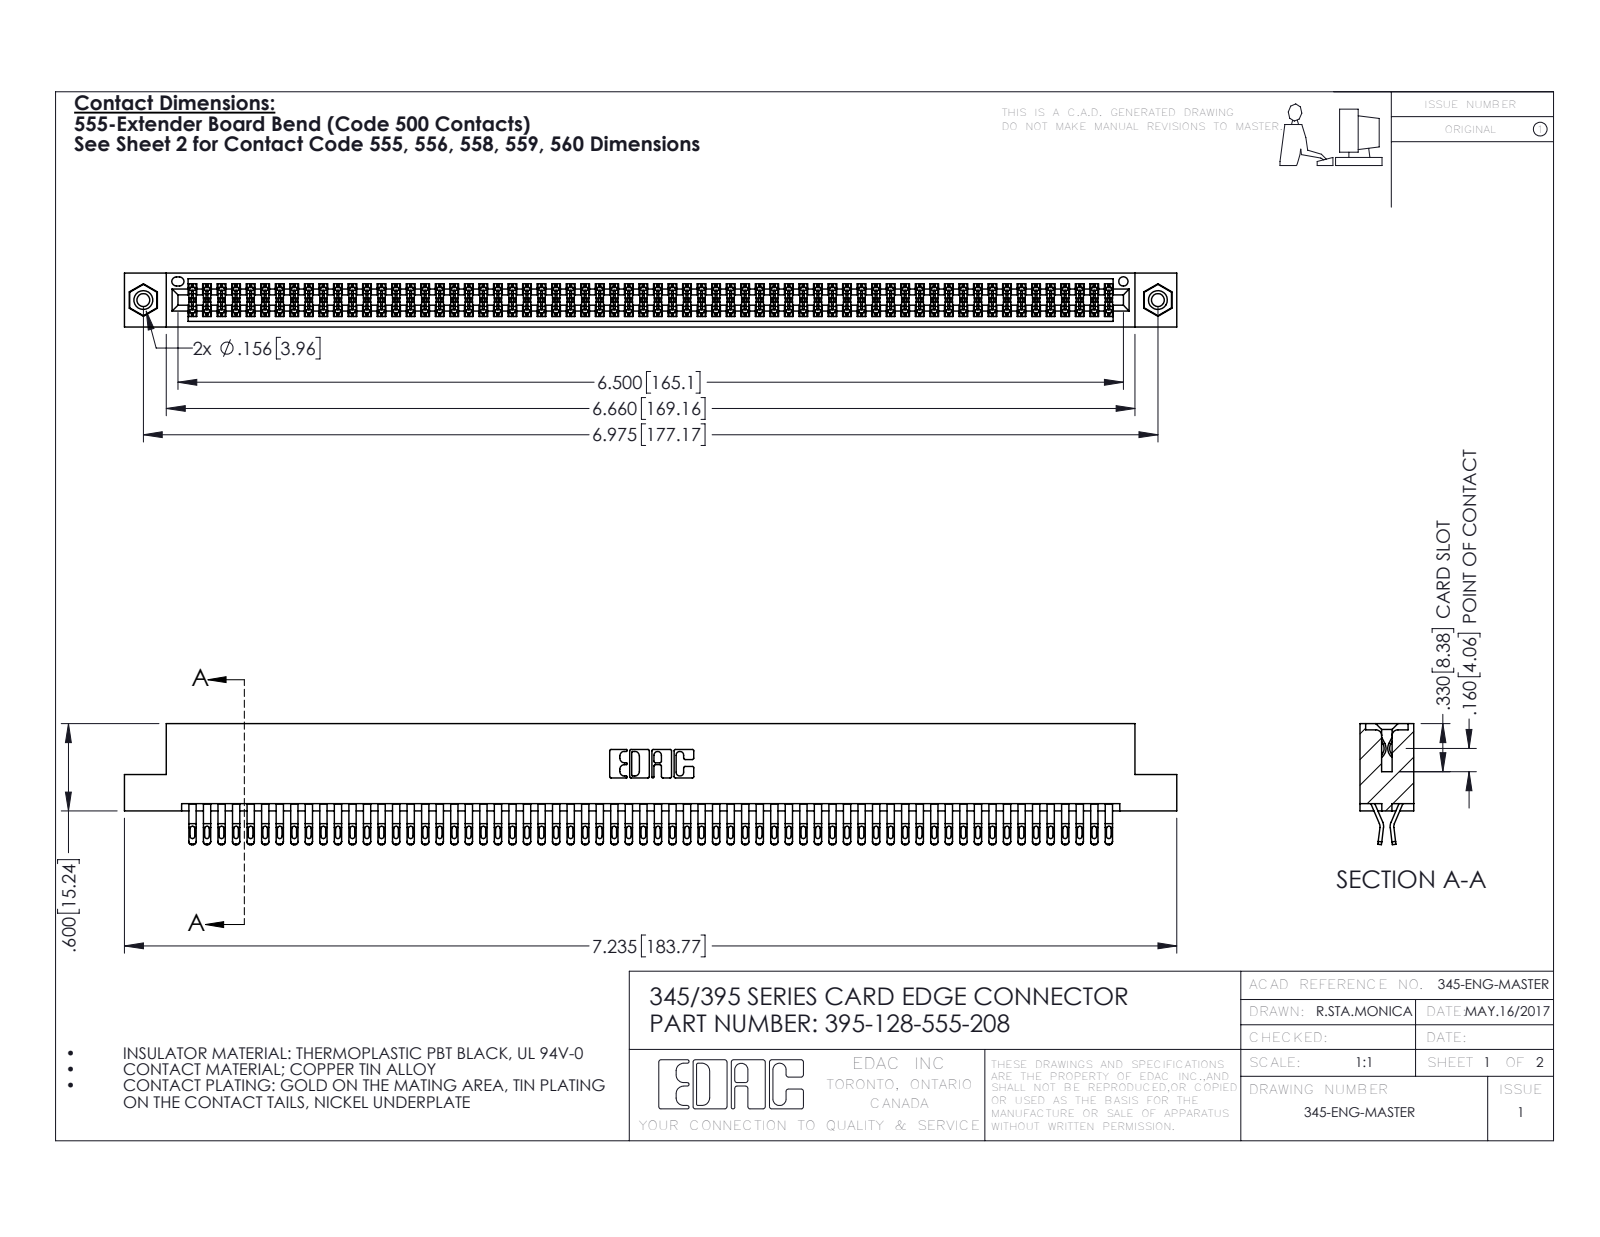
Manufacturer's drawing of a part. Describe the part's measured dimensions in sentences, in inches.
The part is named "345-292-001_555 Tail; 395-128-555-208; 345 Part_Flush Mounting Lugs - 0.156 Dia-TI; 345-250-001_345-250-003-102". Its 3-D file was written by "SolidWorks 2016 (CONFIG_CONTROL_DESIGN)". It is 131 solids with 7354 faces: 4080 planar, 3258 cylindrical and 16 other. Overall it measures 7.235 by 0.832 by 0.37 inches. Its volume is 1.124 cubic inches and its surface area 44.89 square inches. Round holes: 2 of diameter 0.089, 2 of diameter 0.125, 2 of diameter 0.156, 1 of diameter 0.064. Round bosses or shafts: 2 of diameter 0.155. Partial cylindrical surfaces (rounded edges, fillets, slot ends): 320 of radius 0.016, 256 of radius 0.02, 192 of radius 0.006, 22 of radius 0.01, 6 of radius 0.007, 6 of radius 0.031, 3 of radius 0.026, 2 of radius 0.01. The main face-to-face distances are 0.072, 0.298, 0.025, 0.37, 0.2, 0.098, 0.272, 0.225, 0.175, 0.149. The hole center spacings are 0.27, 6.739, 6.975.
